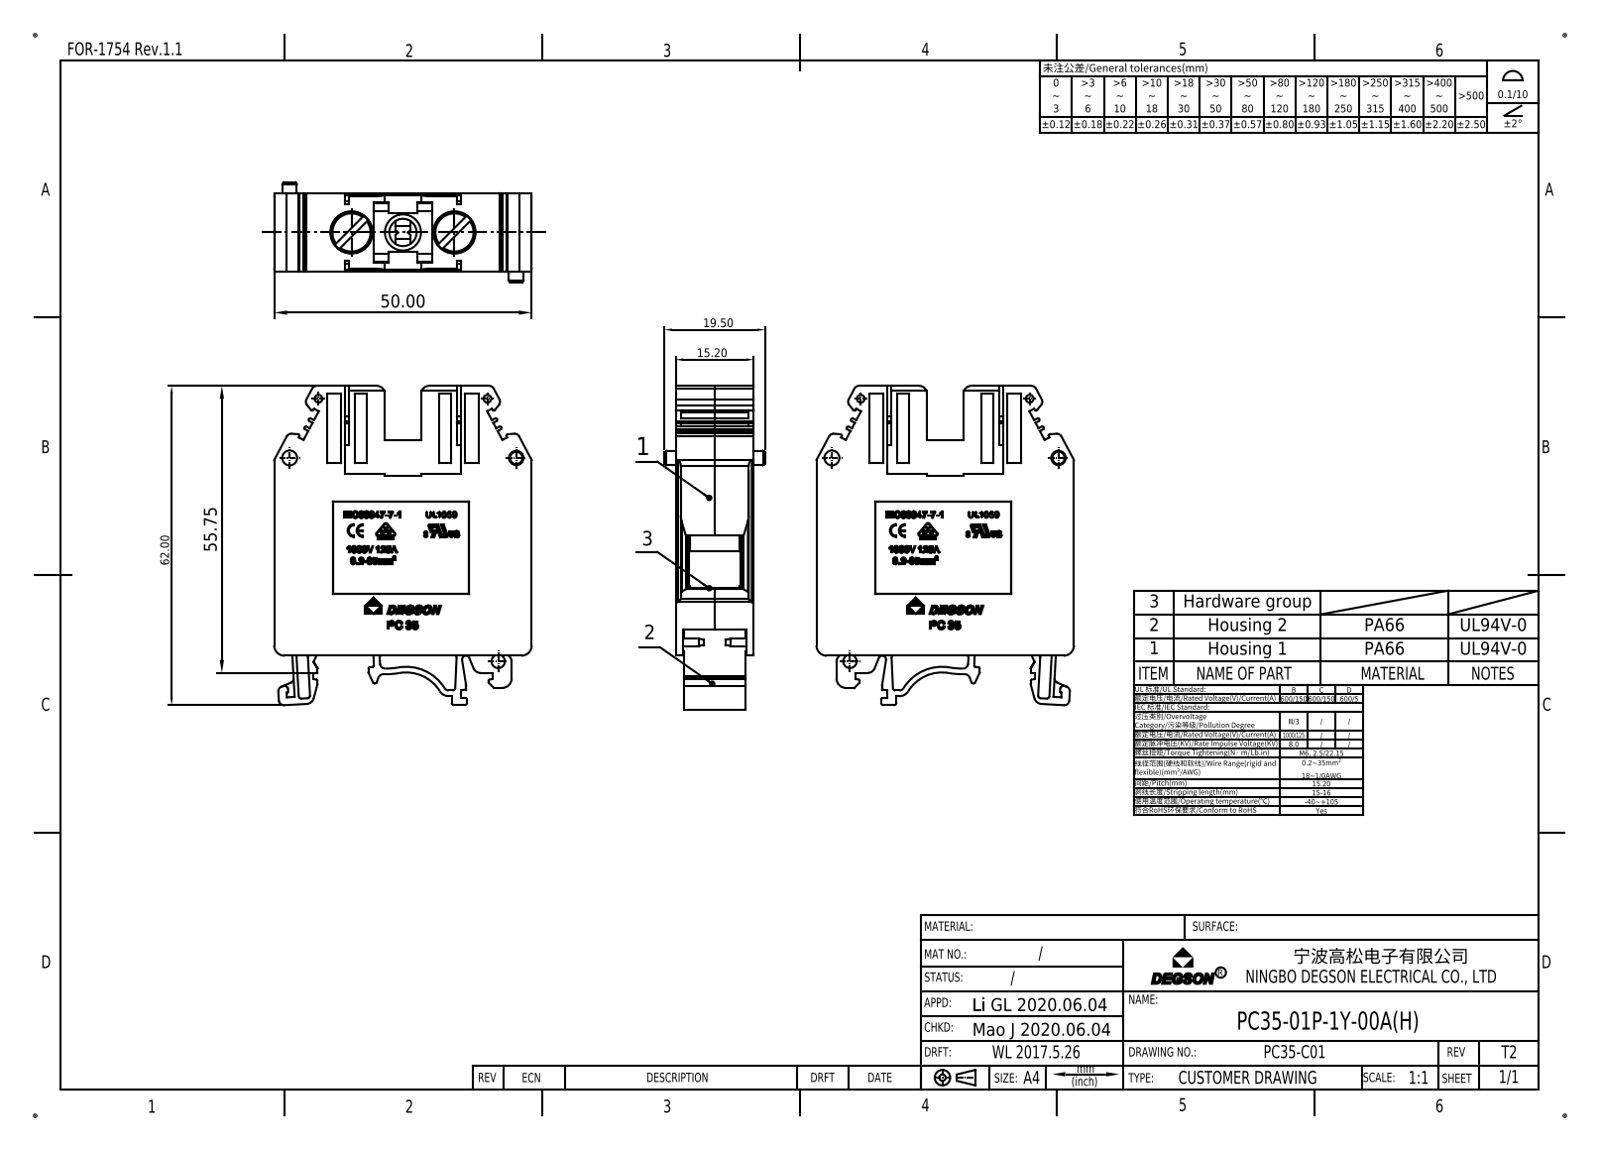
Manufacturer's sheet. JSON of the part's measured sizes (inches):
{"part_name": "PRT0013", "step_written_by": "PRO/ENGINEER BY PARAMETRIC TECHNOLOGY CORPORATION, 2014000 (CONFIG_CONTROL_DESIGN)", "units": "inches", "bodies": {"solids": 1, "faces": 236, "planar": 153, "cylindrical": 79, "other": 4}, "overall_size": [2.441, 1.969, 0.768], "volume_in3": 2.081, "surface_area_in2": 16.69, "round_holes": [[0.268, 2], [0.323, 2]], "round_bosses_or_shafts": [[0.11, 2]], "partial_cylinders_radius": [[0.008, 13], [0.012, 11], [0.024, 9], [0.039, 9], [0.059, 5], [0.004, 4], [0.02, 3], [0.079, 3]], "face_to_face_distances": [0.598, 0.024, 0.039, 0.063, 0.559, 0.535, 0.496, 0.559, 1.004, 0.203], "hole_center_spacings": [0.787]}
